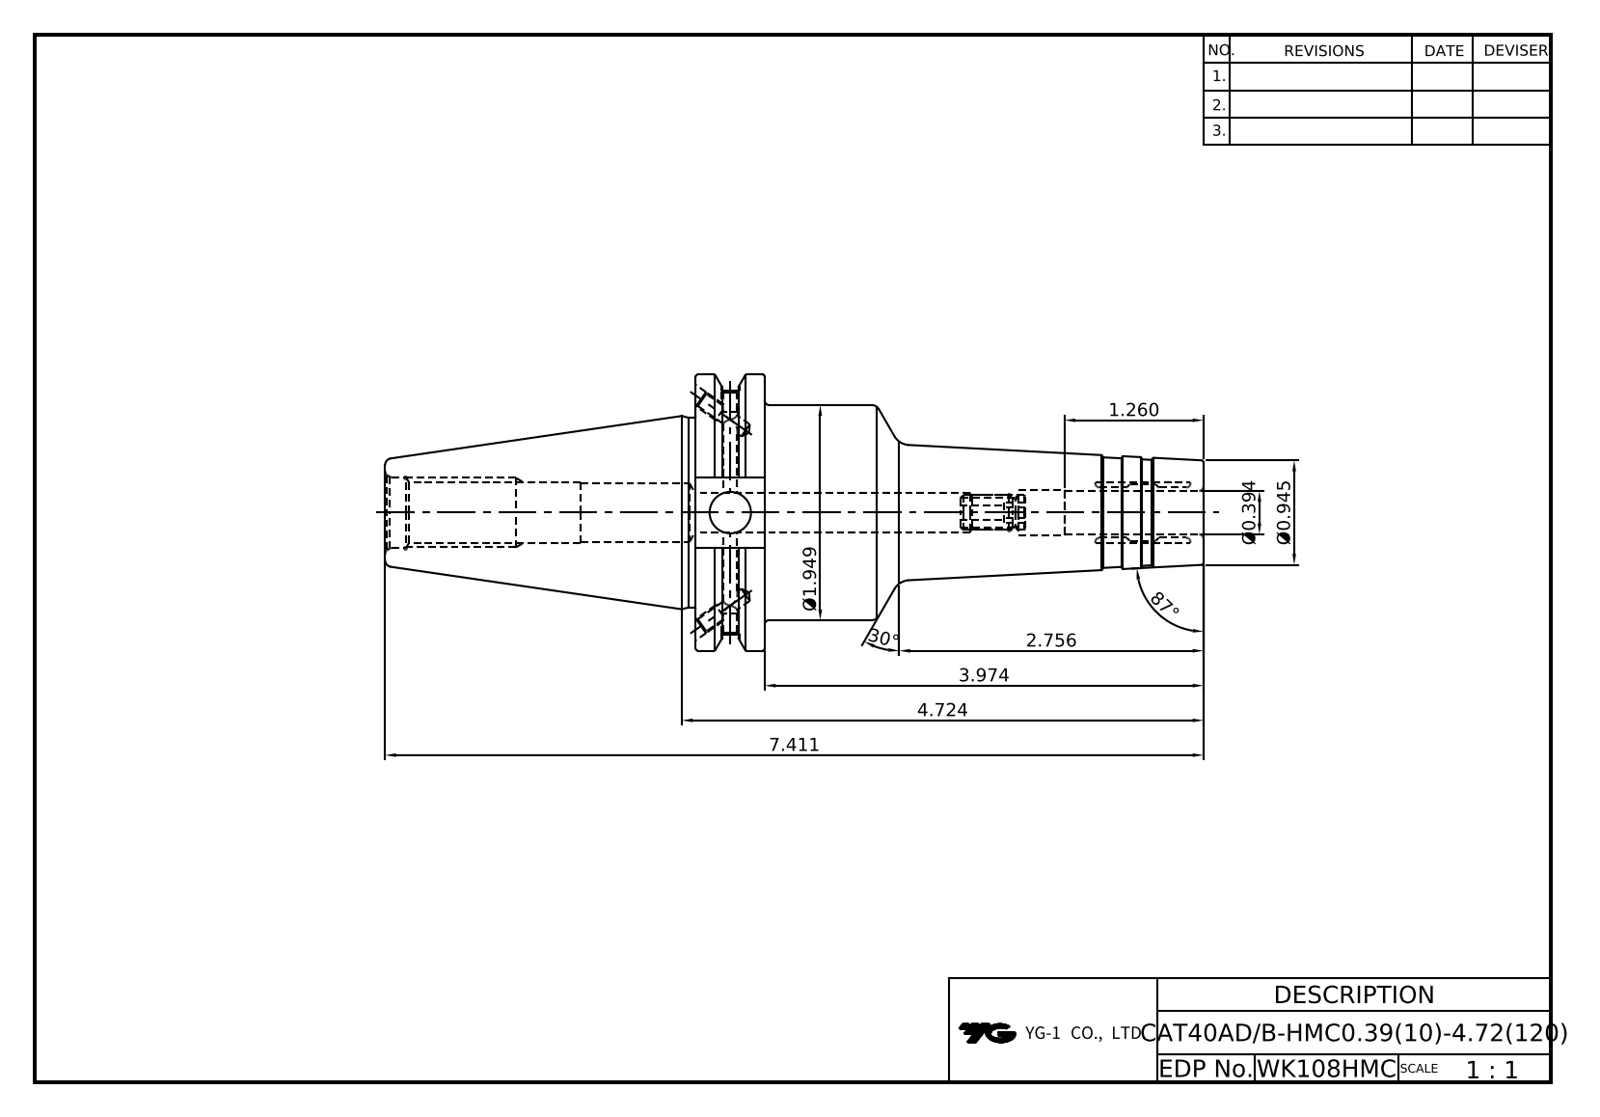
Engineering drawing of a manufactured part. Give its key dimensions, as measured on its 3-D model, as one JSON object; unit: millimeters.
{"part_name": "LO-CAT40ADB-HMC10-120", "step_written_by": "Autodesk Inventor 2020 (AUTOMOTIVE_DESIGN)", "units": "millimeters", "bodies": {"solids": 1, "faces": 108, "planar": 36, "cylindrical": 31, "other": 41}, "overall_size": [188.25, 63.5, 61.09], "volume_mm3": 194329, "surface_area_mm2": 33282, "round_holes": [[3.24, 4], [4, 2], [4.2, 2], [4.92, 1], [8, 1], [9.53, 1], [10, 1], [10.8, 1], [13, 1], [13.39, 1], [16.3, 1]], "round_bosses_or_shafts": [[63.5, 1], [49.5, 1], [43.6, 1]], "partial_cylinders_radius": [[8.19, 1], [28.15, 1]], "face_to_face_distances": [15.88, 116.83, 100.95, 47.6, 16.38, 71.42, 87.3, 188.25, 77.47, 6.05]}
